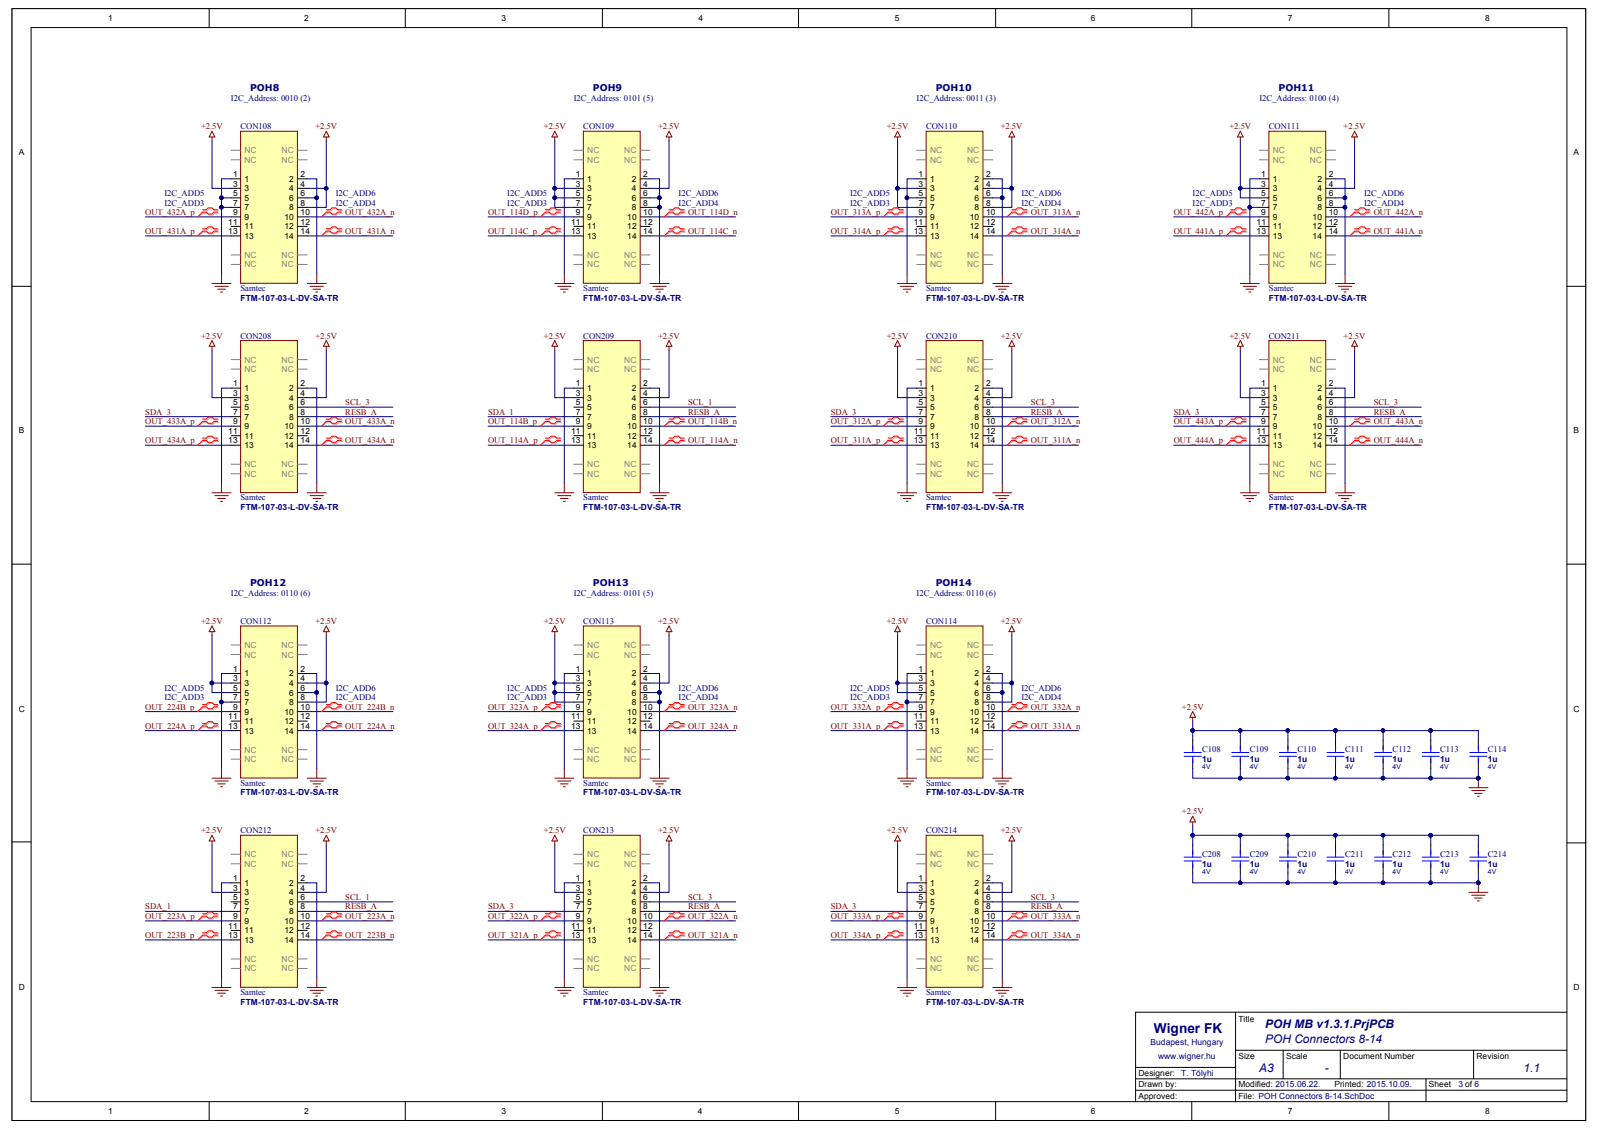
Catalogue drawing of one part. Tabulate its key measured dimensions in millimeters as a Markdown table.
| quantity | value |
| --- | --- |
| part name | PCB; BoardPOH_MB_v1.3.1; R4POH_MB_v1.3.1; 0603-R (+8 more) |
| STEP written by | Open CASCADE 6.5 (AUTOMOTIVE_DESIGN) |
| units | millimeters |
| bodies | 83 solids, 8343 faces (7255 planar, 784 cylindrical, 304 other) |
| overall size | 685 × 41 × 6.74 |
| volume | 20 541 mm³ |
| surface area | 69 667 mm² |
| round holes (diameter × count) | 1.13 × 56, 0.7 × 16, 0.64 × 4, 0.9 × 4 |
| round bosses / shafts (diameter × count) | 1 × 56 |
| partial cylindrical surfaces (radius × count) | 1 × 36 |
| main face-to-face distances | 0.56, 33.4, 4.13, 3.57, 4.44, 1.58, 0.33, 6.02, 34.98, 39.42 |
| hole center spacings | 40, 80, 13, 52.11, 120, 27, 53, 86.69 |
